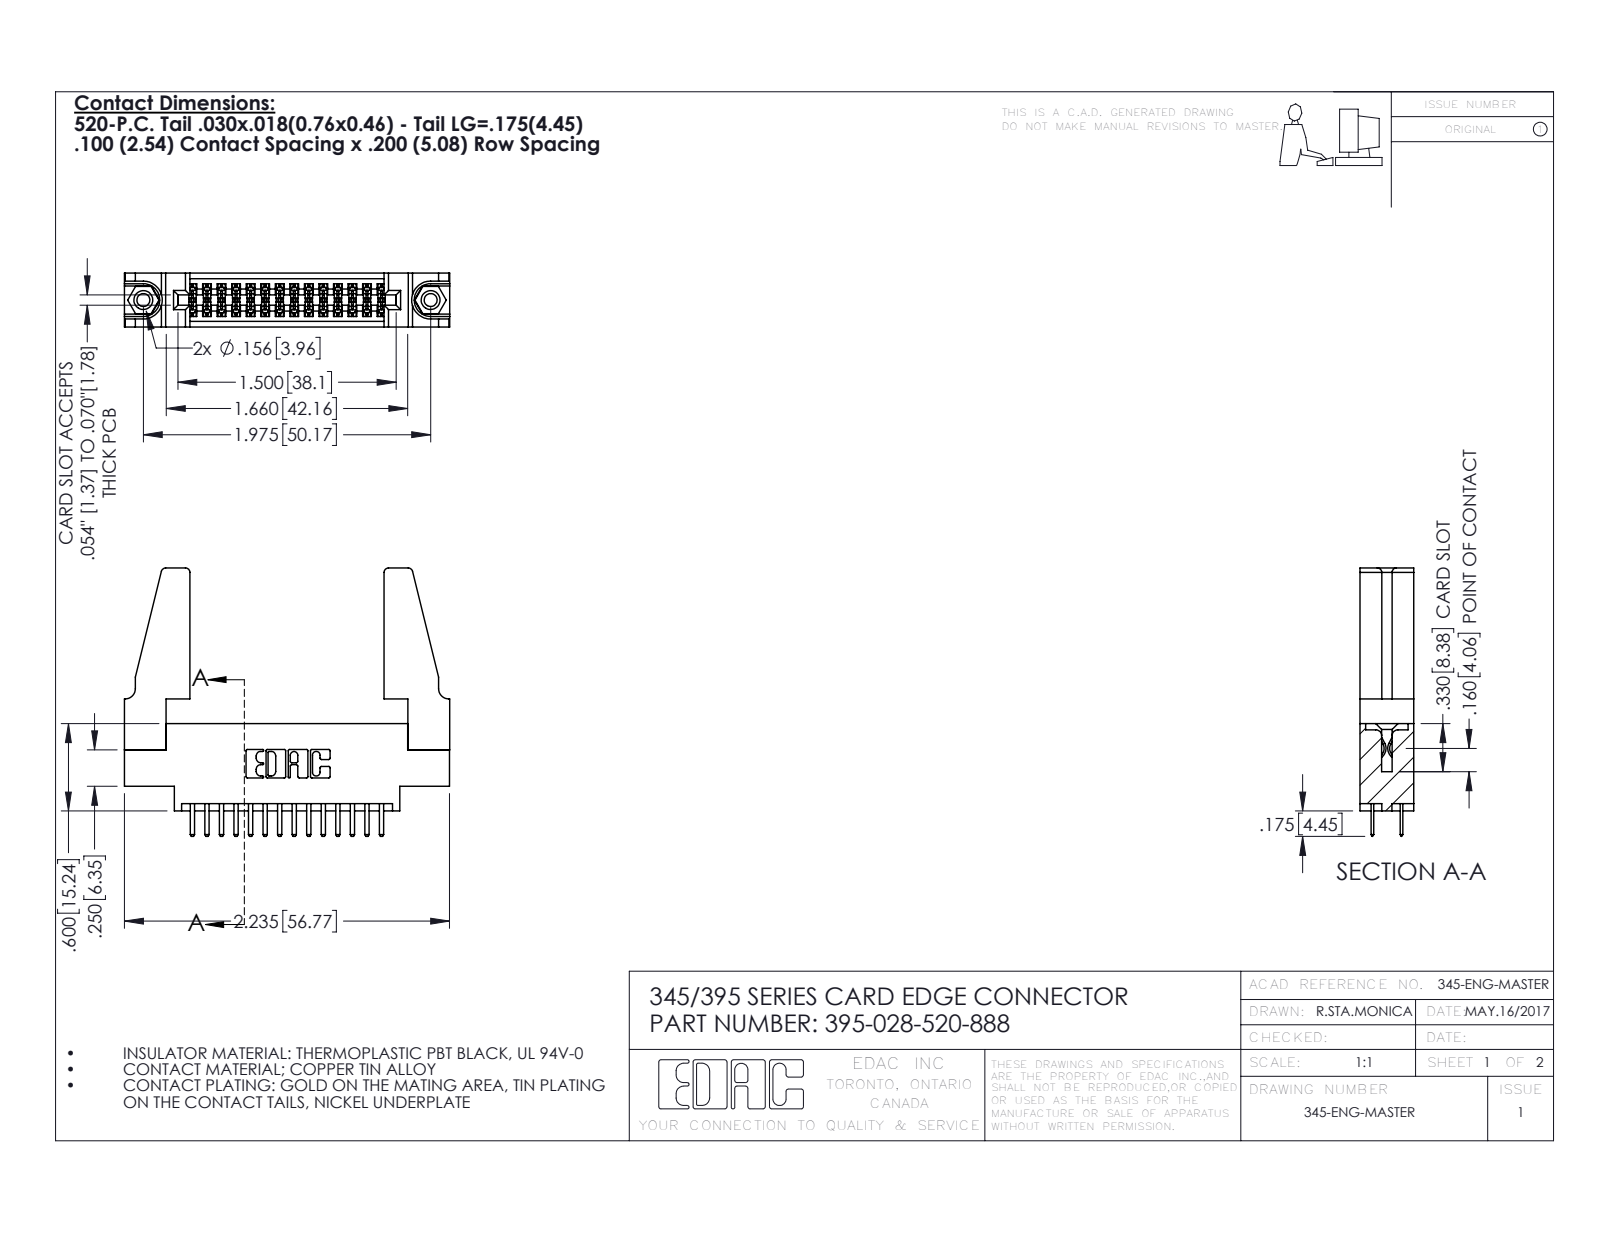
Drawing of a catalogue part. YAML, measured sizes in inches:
part_name: "345-292-001_345-293-120; 345-250-001_345-250-001-102; 345-220-078_345-220-088; 345 Part_0.170 Offset - 0.156 Dia-TH (+1 more)"
step_written_by: "SolidWorks 2016 (CONFIG_CONTROL_DESIGN)"
units: inches
bodies: {solids: 33, faces: 1766, planar: 1136, cylindrical: 614, other: 16}
overall_size: [2.236, 1.845, 0.37]
volume: 0.512
surface_area: 15.94
round_holes:
  - {diameter: 0.089, count: 2}
  - {diameter: 0.125, count: 2}
  - {diameter: 0.156, count: 2}
  - {diameter: 0.064, count: 1}
round_bosses_or_shafts:
  - {diameter: 0.155, count: 2}
partial_cylinders:
  - {radius: 0.006, count: 42}
  - {radius: 0.01, count: 32}
  - {radius: 0.01, count: 22}
  - {radius: 0.03, count: 8}
  - {radius: 0.007, count: 6}
  - {radius: 0.031, count: 6}
  - {radius: 0.026, count: 3}
  - {radius: 0.014, count: 2}
face_to_face_distances: [0.37, 0.072, 0.298, 0.2, 0.098, 0.272, 0.025, 0.225, 0.022, 0.175]
hole_center_spacings: [0.27, 1.742, 1.975]
